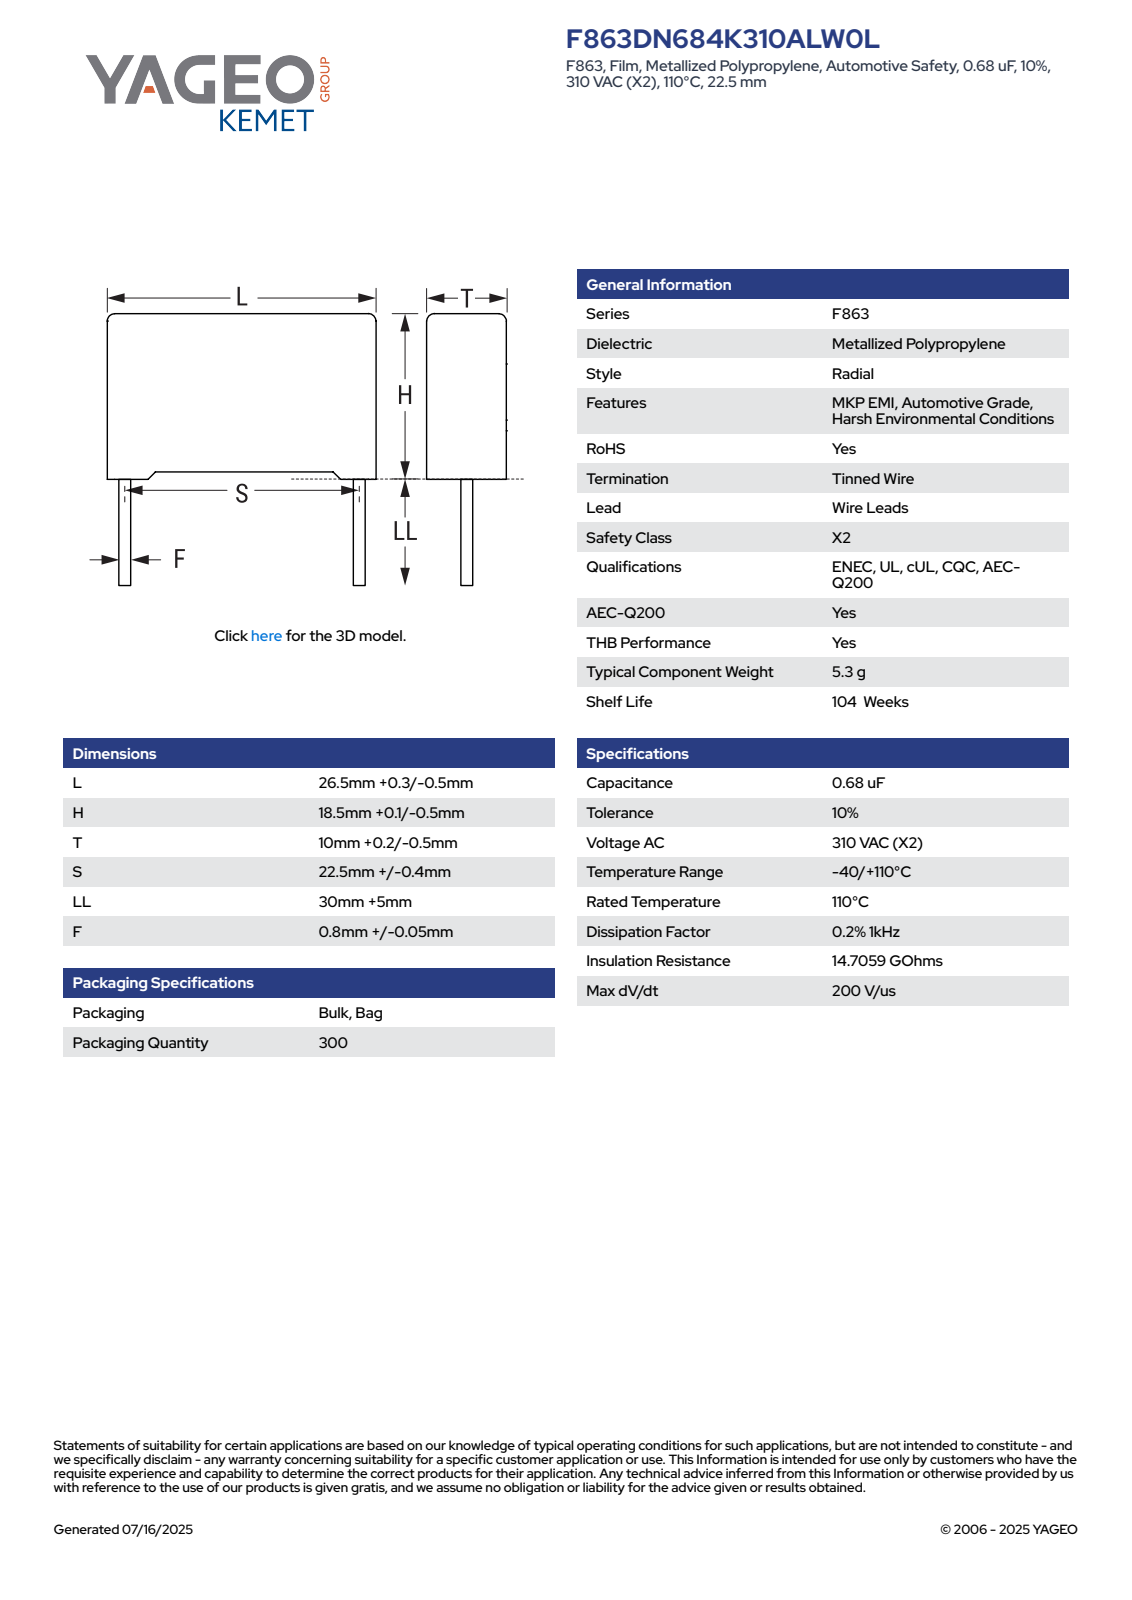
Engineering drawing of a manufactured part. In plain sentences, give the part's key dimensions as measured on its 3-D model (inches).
The part is named "CFR_RB_26.5X18.5X10_L26.8H18.6T10.2S22.5LL35F0.85". Its 3-D file was written by "SolidWorks 2014 (AUTOMOTIVE_DESIGN)". It is 4 solids with 89 faces: 81 planar, 8 cylindrical and 0 other. Overall it measures 2.11 by 1.055 by 0.402 inches. Its volume is 0.299 cubic inches and its surface area 3.271 square inches. Round bosses or shafts: 2 of diameter 0.033. Partial cylindrical surfaces (rounded edges, fillets, slot ends): 4 of radius 0.026. The main face-to-face distances are 0.402, 0.699, 1.055, 0.024, 0.378, 0.033, 0.732, 0.354, 0.583, 1.378.
